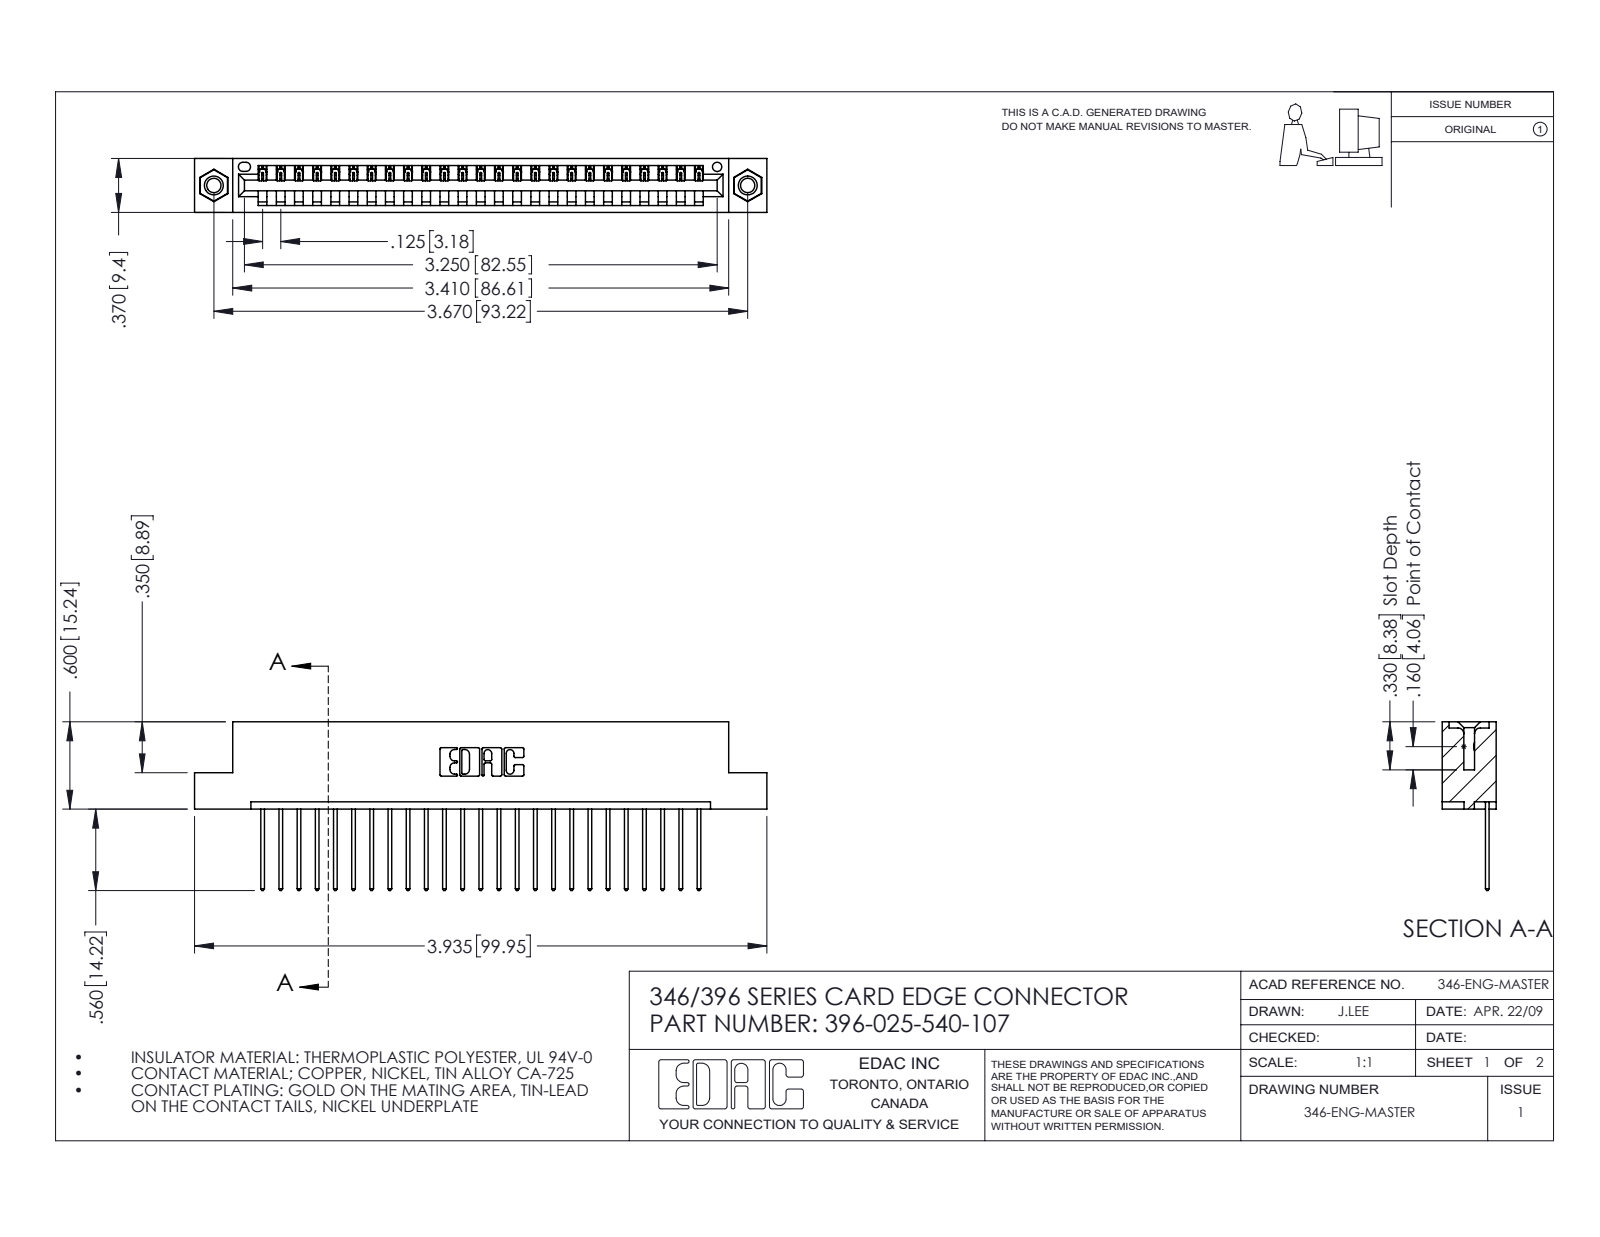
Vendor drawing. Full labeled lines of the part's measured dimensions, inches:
Part name (STEP PRODUCT): 345-250-001_345-250-005-103; 396-025-540-107; 345-292-001_345-293-140; 346 Part_Flush Mounting Lugs - 0.156 Dia-TI
STEP written by: SolidWorks 2016 (CONFIG_CONTROL_DESIGN)
Units: inches
Bodies: 28 solids, 1632 faces (1108 planar, 508 cylindrical, 16 other)
Overall size (bounding box): 3.935 × 1.16 × 0.37
Volume: 0.578 in³ · Surface area: 18.5 in²
Round holes (diameter × count): ⌀0.098 ×2, ⌀0.125 ×2, ⌀0.156 ×2, ⌀0.064 ×1
Round bosses / shafts (diameter × count): ⌀0.155 ×2
Partial cylindrical surfaces — rounded edges, fillets, slot ends (radius × count): R0.006 ×50, R0.01 ×50, R0.01 ×22, R0.007 ×6, R0.031 ×6, R0.026 ×3, R0.031 ×2, R0.04 ×2
Main face-to-face distances: 0.048, 0.322, 0.37, 0.25, 0.072, 0.298, 0.025, 0.148, 0.222, 0.1
Hole centre spacings: 0.246, 3.462, 3.67
